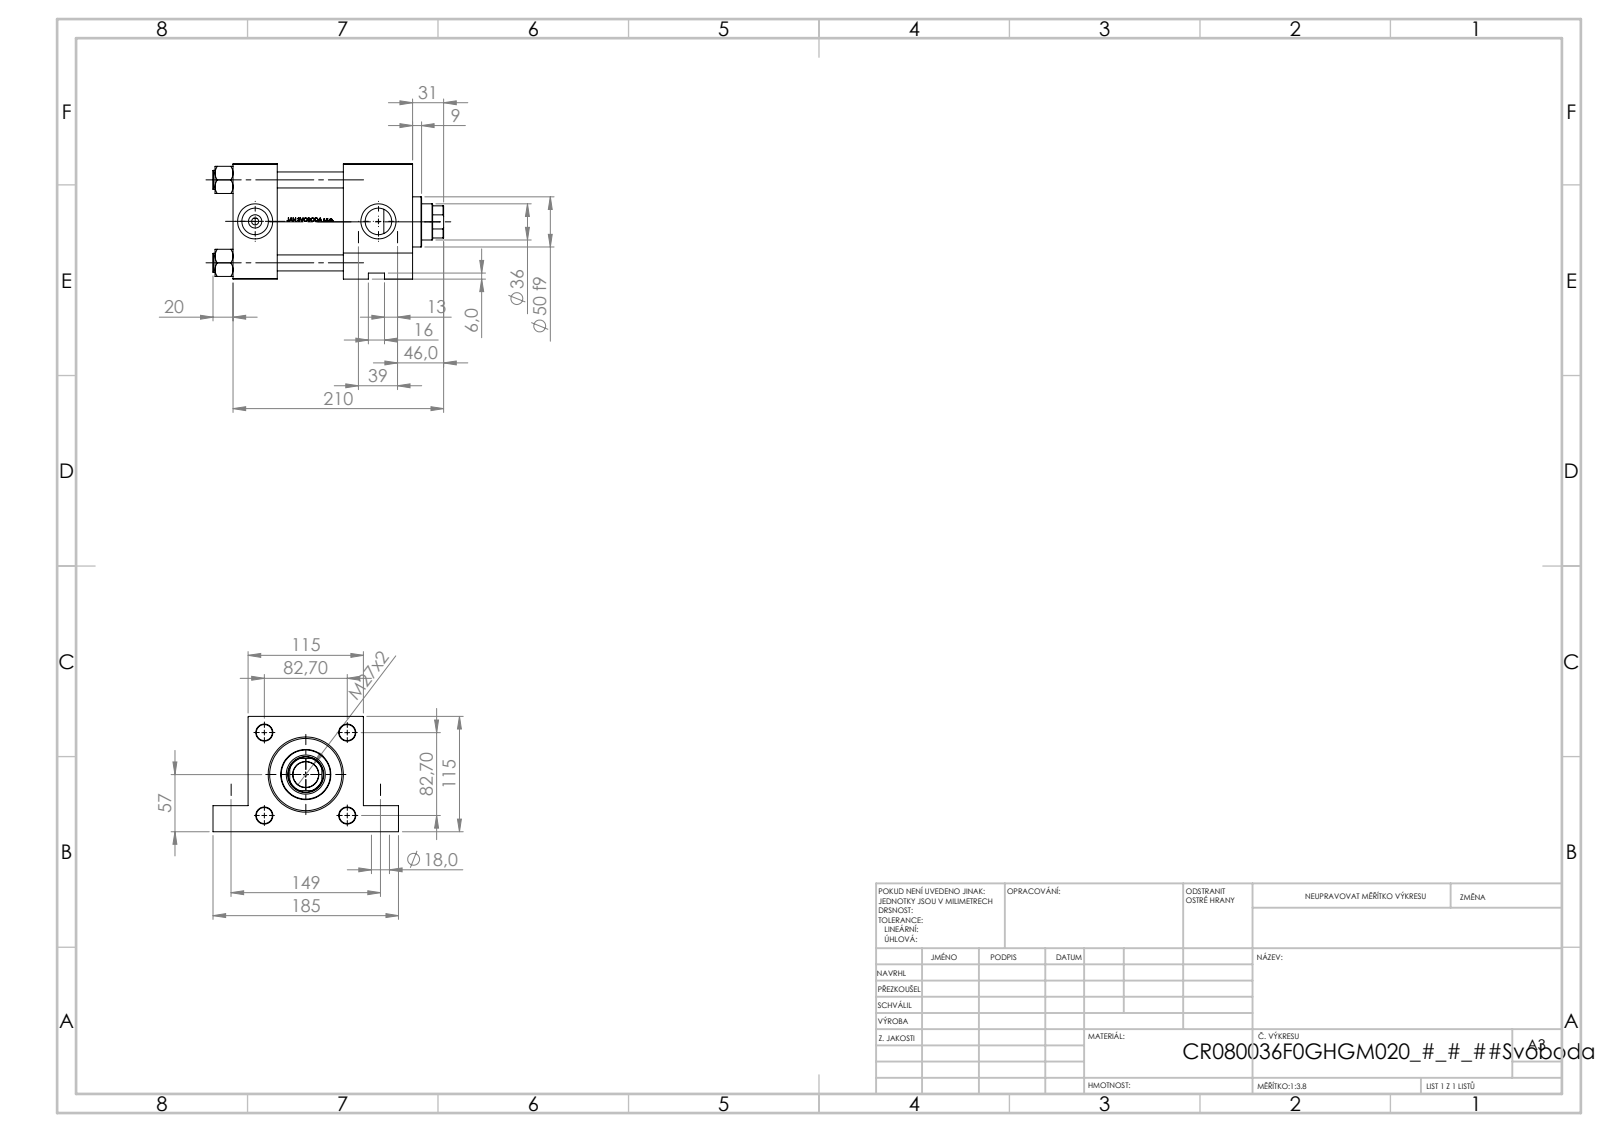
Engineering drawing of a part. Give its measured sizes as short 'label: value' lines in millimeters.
name: V215CR_VCP_F; V215_VC_A; NUT_M5_F; V215CR_F_Body (+1 more)
written by: SolidWorks 2019 (CONFIG_CONTROL_DESIGN)
unit: mm
bodies: 11 solids, 1151 faces (485 planar, 126 cylindrical, 540 other)
size: 230 × 185 × 115
volume: 1 883 000 mm³; area: 283 577 mm²
holes: 4× ⌀16, 4× ⌀18, 2× ⌀7, 2× ⌀26.44, 2× ⌀35, 1× ⌀25.5, 1× ⌀36, 1× ⌀39, 1× ⌀61, 1× ⌀72, 1× ⌀80
bosses: 4× ⌀19, 1× ⌀86, 1× ⌀50
rounds: 1× R17.5
face distances: 115, 44, 135, 179, 110, 66, 69, 20, 89, 150.3
hole spacings: 82.7, 39, 58.13, 58.83, 116.96, 149, 154.02, 123
